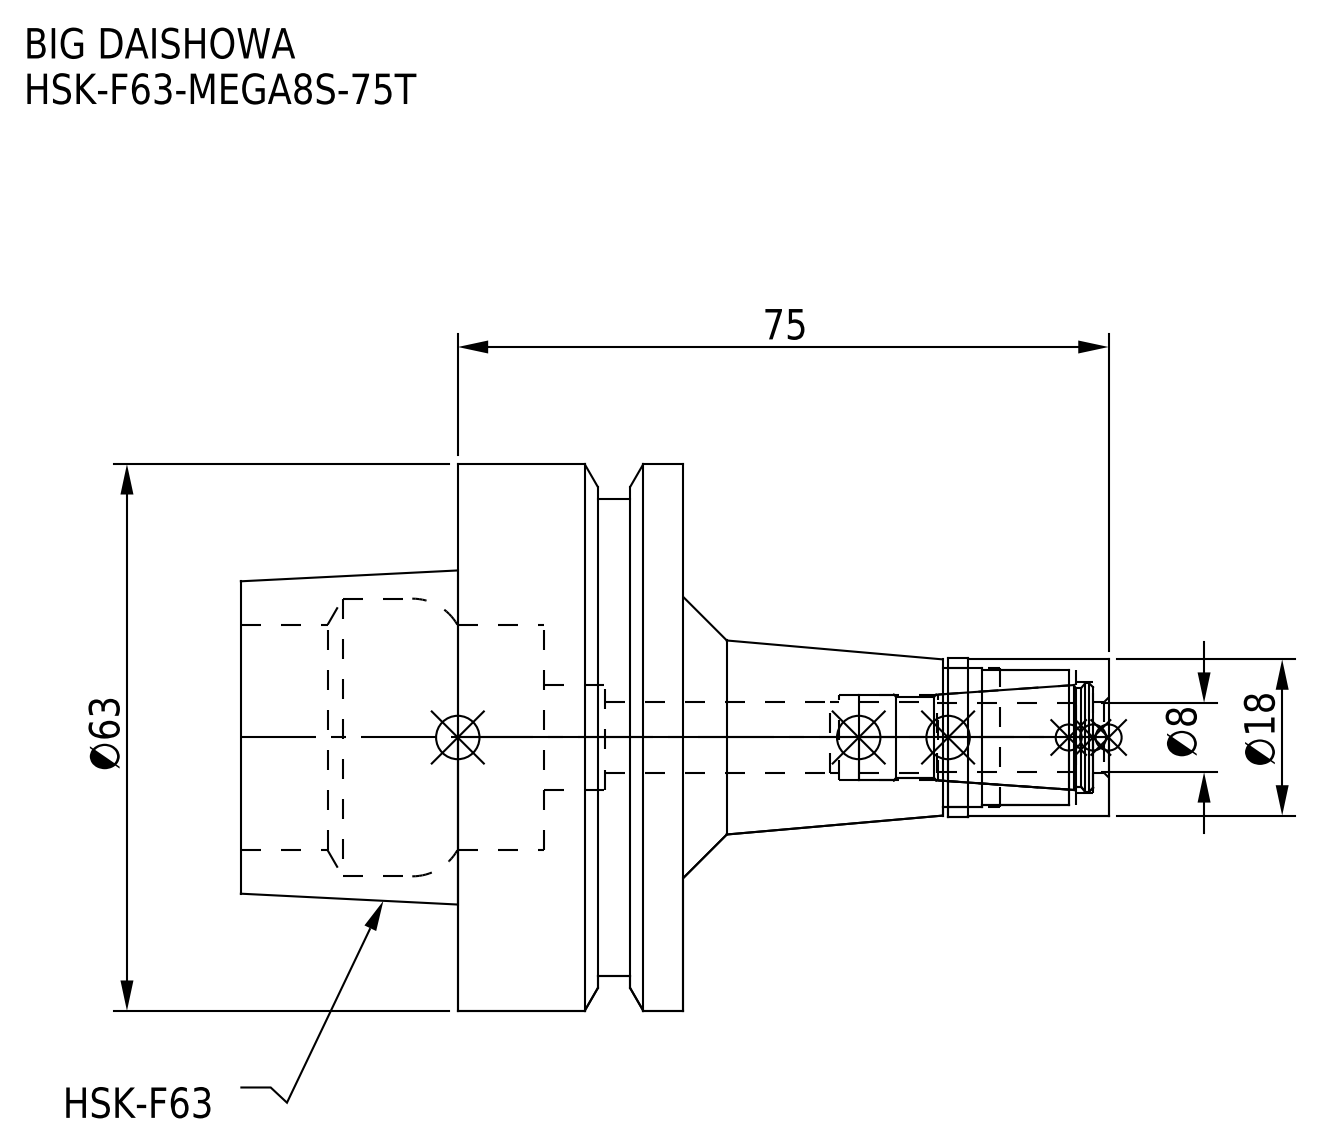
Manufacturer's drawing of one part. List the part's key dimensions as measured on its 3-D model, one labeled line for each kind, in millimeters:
Part name (STEP PRODUCT): HSK-F63-MEGA8S-75T-080.stp; HSK-F63-MEGA8S-75T-080-FreeParts; HF63MS08075T-080_ASM.stp; DXF_TEMP_ASSY_ASM_4_ASM.stp (+3 more)
STEP written by: SolidWorks 2019 (CONFIG_CONTROL_DESIGN)
Units: millimetres
Bodies: 2 solids, 74 faces (18 planar, 38 cylindrical, 18 other)
Overall size (bounding box): 100 × 63 × 63
Volume: 93 548 mm³ · Surface area: 24 813 mm²
Round holes (diameter × count): ⌀8.2 ×1, ⌀8.25 ×1, ⌀9.9 ×1, ⌀12 ×1, ⌀12.9 ×1, ⌀15.6 ×1, ⌀16.1 ×1, ⌀26 ×1, ⌀32 ×1
Round bosses / shafts (diameter × count): ⌀63 ×1, ⌀55 ×1, ⌀18.3 ×1, ⌀18 ×1
Main face-to-face distances: 26, 51, 25, 16.05, 9.95, 34.95, 9.88, 6.17, 16.12, 41.12
